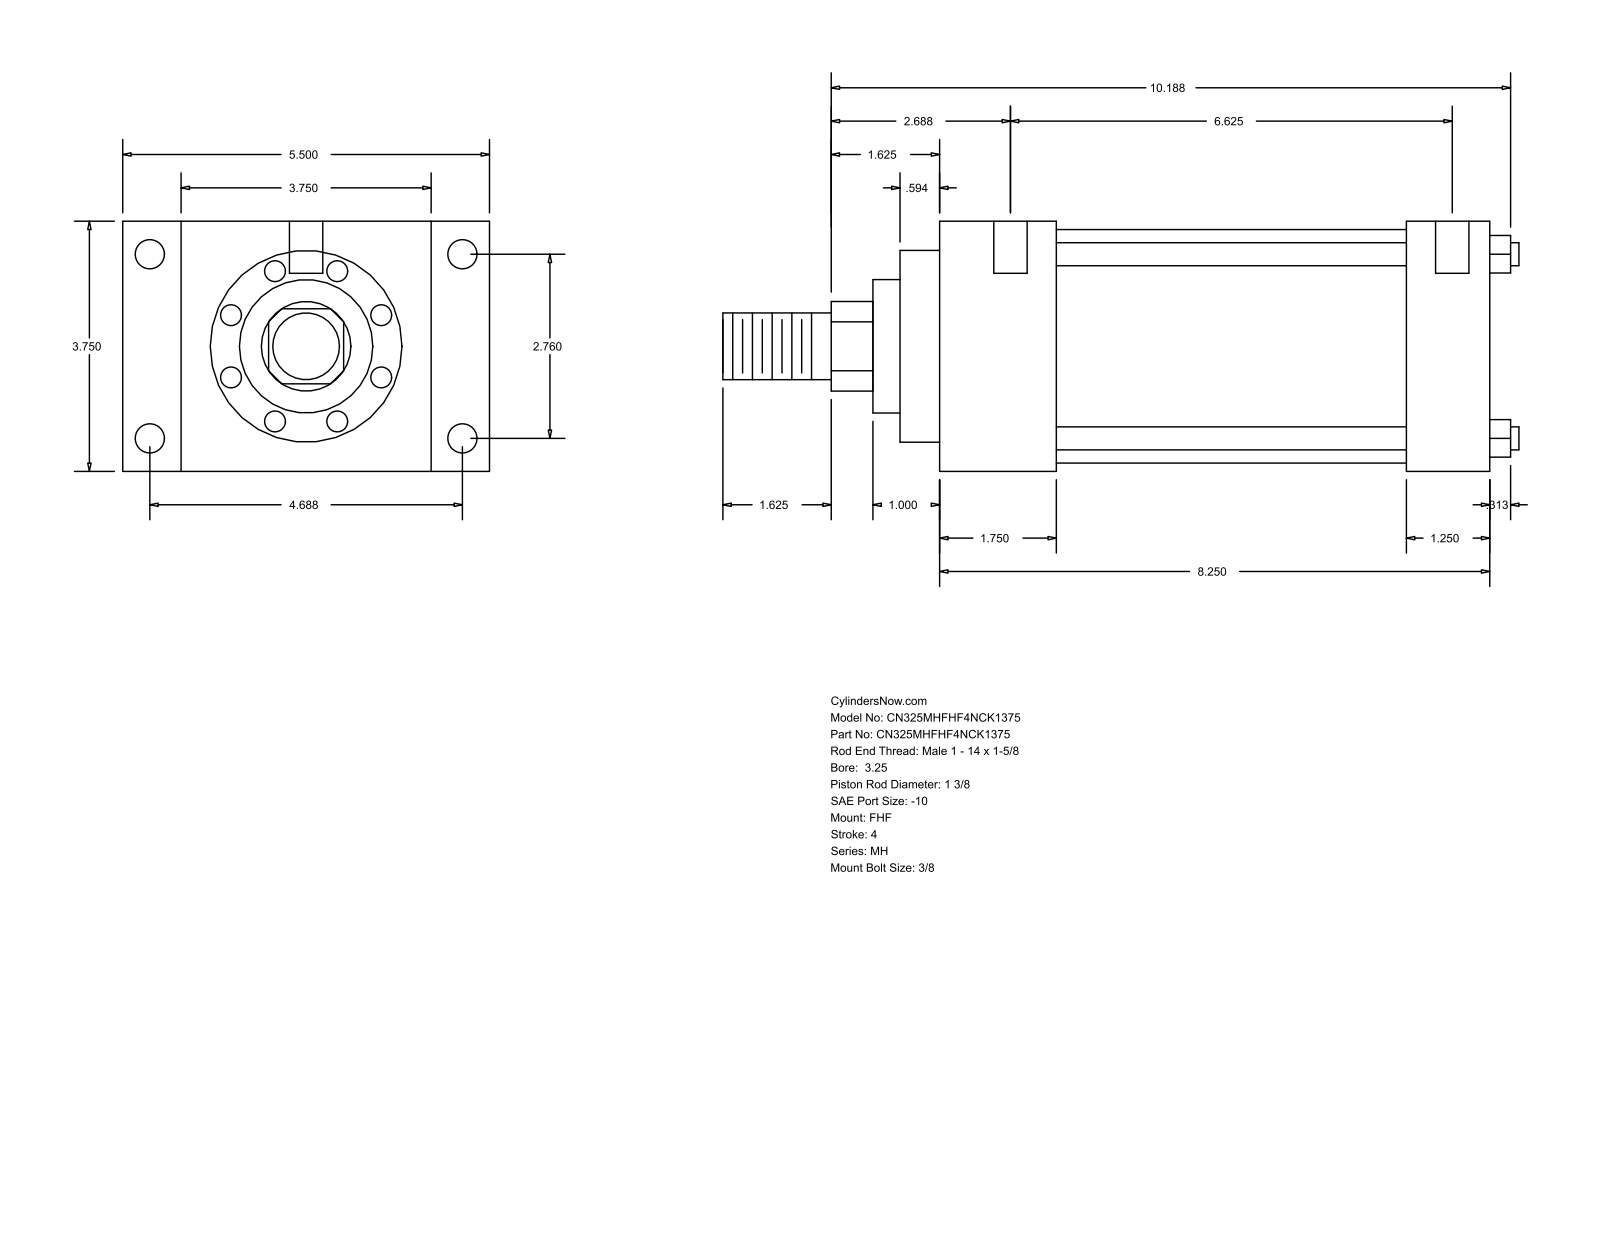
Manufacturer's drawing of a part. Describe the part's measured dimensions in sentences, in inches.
The part is named "MH_FHF__0325_1.375". Its 3-D file was written by "GSSL Pune (CONFIG_CONTROL_DESIGN)". It is 0 solids with 90 faces: 61 planar, 29 cylindrical and 0 other. Overall it measures 11.937 by 5.5 by 3.75 inches. Round holes: 4 of diameter 0.219, 4 of diameter 0.438, 2 of diameter 0.5. Round bosses or shafts: 4 of diameter 0.345, 1 of diameter 3.5, 1 of diameter 2.875, 1 of diameter 2, 1 of diameter 1.375, 1 of diameter 1. Partial cylindrical surfaces (rounded edges, fillets, slot ends): 1 of radius 0.672. The main face-to-face distances are 3.75, 8.25, 1.75, 6.5, 0.875, 4.625, 5.5, 7, 5.25, 1.25. The hole center spacings are 2.76, 4.687, 5.439, 6.875, 0.063, 0.187, 6.625, 6.688.
